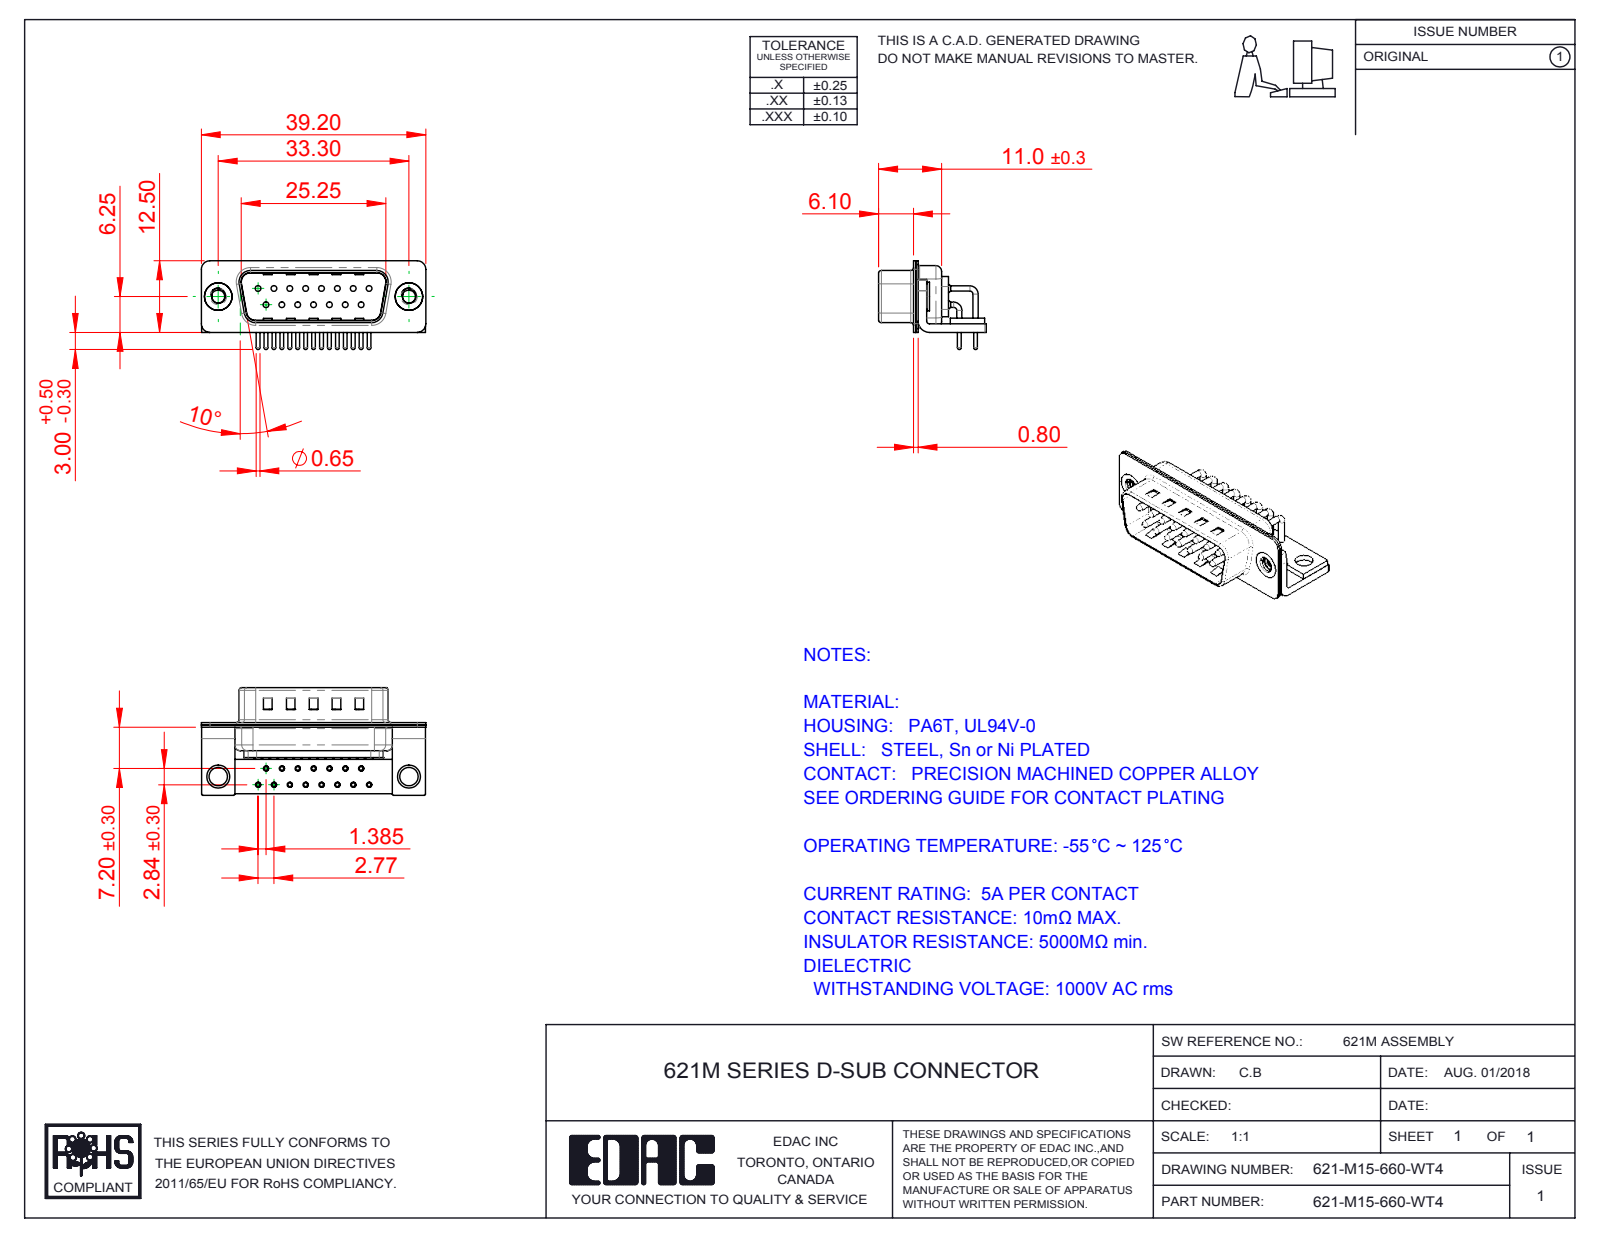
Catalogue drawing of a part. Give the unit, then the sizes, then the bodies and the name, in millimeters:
Units: millimetres
Overall size (bounding box): 39.2 × 18.8 × 15.49
Round holes (diameter × count): ⌀0.9 ×15, ⌀1 ×15, ⌀1.7 ×15, ⌀2 ×15, ⌀2.26 ×2, ⌀3.2 ×2, ⌀4 ×2, ⌀4.8 ×2
Round bosses / shafts (diameter × count): ⌀0.9 ×22, ⌀1.5 ×15, ⌀0.65 ×15, ⌀5 ×2, ⌀4.9 ×2
Partial cylindrical surfaces — rounded edges, fillets, slot ends (radius × count): R0.25 ×16, R1.5 ×16, R1.01 ×15, R2 ×13, R0.5 ×9, R1.6 ×8, R0.6 ×4, R0.65 ×4
Main face-to-face distances: 0.4, 0.85, 1.5, 0.8, 1.25, 10.4, 9.55, 1, 2.1, 1.9
Hole centre spacings: 3.16, 2.77, 5.54, 8.31, 11.08, 5.03, 5.04, 7.48
Volume: 2 371 mm³ · Surface area: 6 349 mm²
Bodies: 23 solids, 2070 faces (1125 planar, 725 cylindrical, 220 other)
Part name (STEP PRODUCT): 621M Contact Row 1; 621M Housing_15 Contacts; 621-M15-660-WT4; 621M 4-40 Threaded Rivet_Stabilizer (+5 more)
STEP written by: SolidWorks 2016 (CONFIG_CONTROL_DESIGN)
